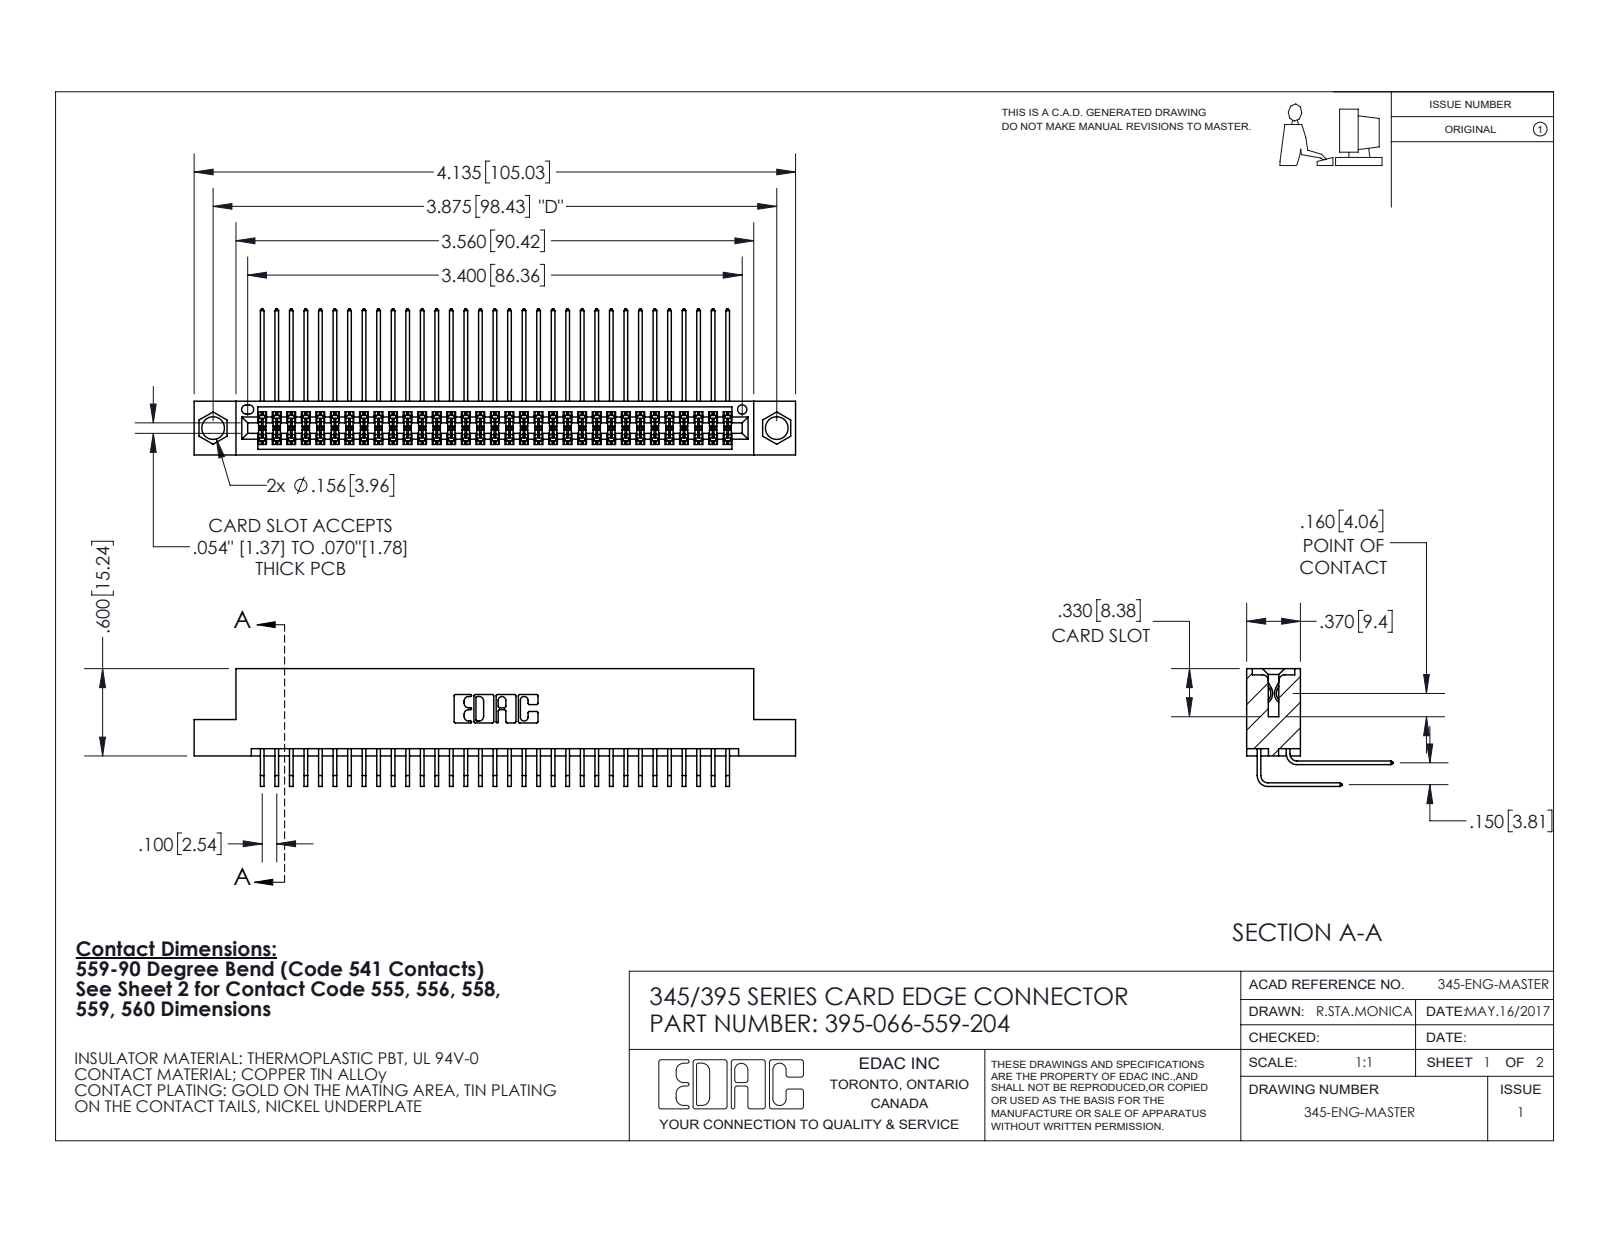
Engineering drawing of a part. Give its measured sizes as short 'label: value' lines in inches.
name: 345-292-001_558 559 Tail - 1; 345-292-001_559 Tail - 2; 395-066-559-204; 345 Part_Flush Mounting Lugs - 0.156 Dia-TI
written by: SolidWorks 2020 (CONFIG_CONTROL_DESIGN)
unit: in
bodies: 67 solids, 3572 faces (2404 planar, 1168 cylindrical, 0 other)
size: 4.135 × 1.005 × 0.809
volume: 0.634 in³; area: 26.09 in²
holes: 2× ⌀0.156, 1× ⌀0.064
rounds: 99× R0.006, 22× R0.01, 6× R0.007, 6× R0.031, 3× R0.026, 2× R0.014, 2× R0.019, 2× R0.022
face distances: 0.072, 0.298, 0.2, 0.37, 0.098, 0.272, 0.025, 0.225, 0.175, 0.15
hole spacings: 0.27, 3.64, 3.875
